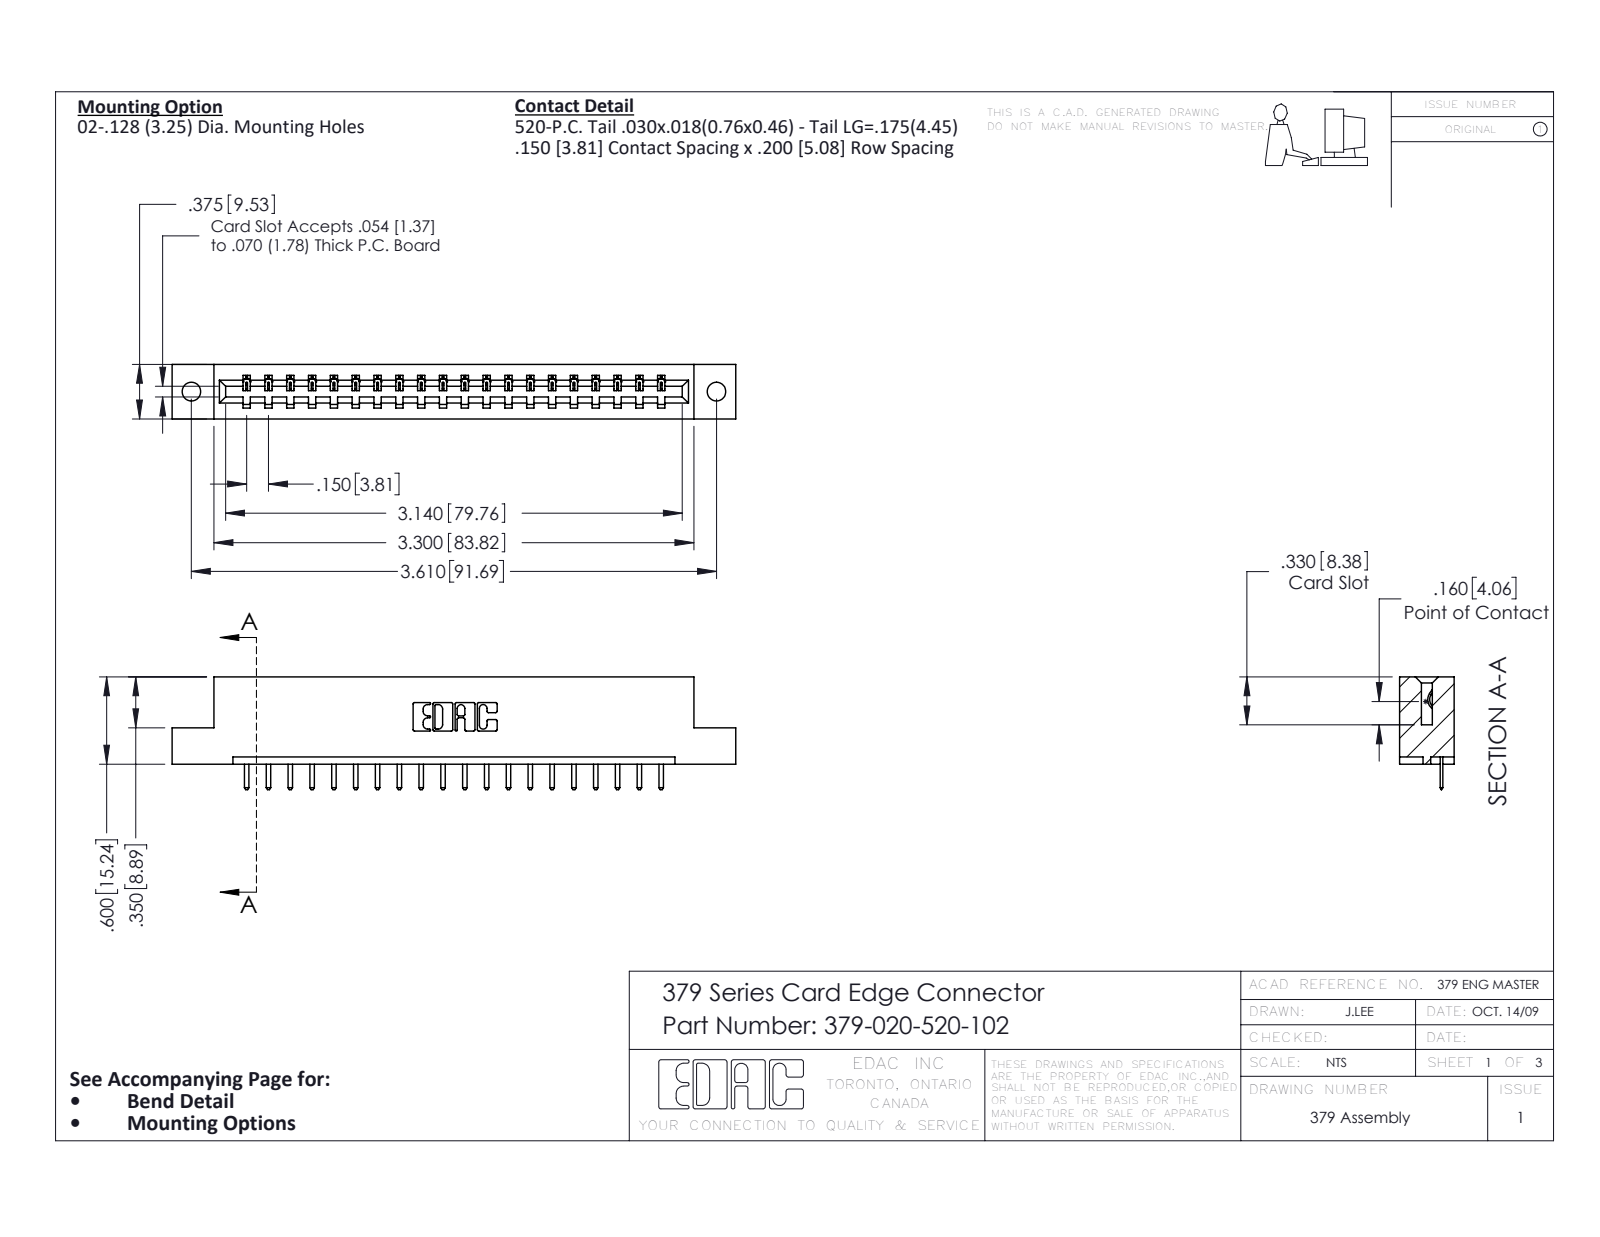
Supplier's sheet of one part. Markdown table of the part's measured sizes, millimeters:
| quantity | value |
| --- | --- |
| part name | 379 Part_Flush - .128 Dia; 379-020-520-102; 345-292-001_345-293-120 |
| STEP written by | SolidWorks 2016 (CONFIG_CONTROL_DESIGN) |
| units | millimeters |
| bodies | 21 solids, 1354 faces (950 planar, 404 cylindrical, 0 other) |
| overall size | 98.4 × 19.7 × 9.5 |
| volume | 9 980 mm³ |
| surface area | 9 626 mm² |
| round holes (diameter × count) | 3.3 × 2 |
| partial cylindrical surfaces (radius × count) | 0.3 × 42, 0.2 × 40, 0.3 × 22, 0.2 × 6, 0.8 × 6, 0.7 × 3, 0.4 × 1, 0.6 × 1 |
| main face-to-face distances | 7.6, 9.5, 1.9, 15.2, 5.7, 3.8, 11.4, 5.1, 19.1, 14 |
| hole center spacings | 91.7 |
